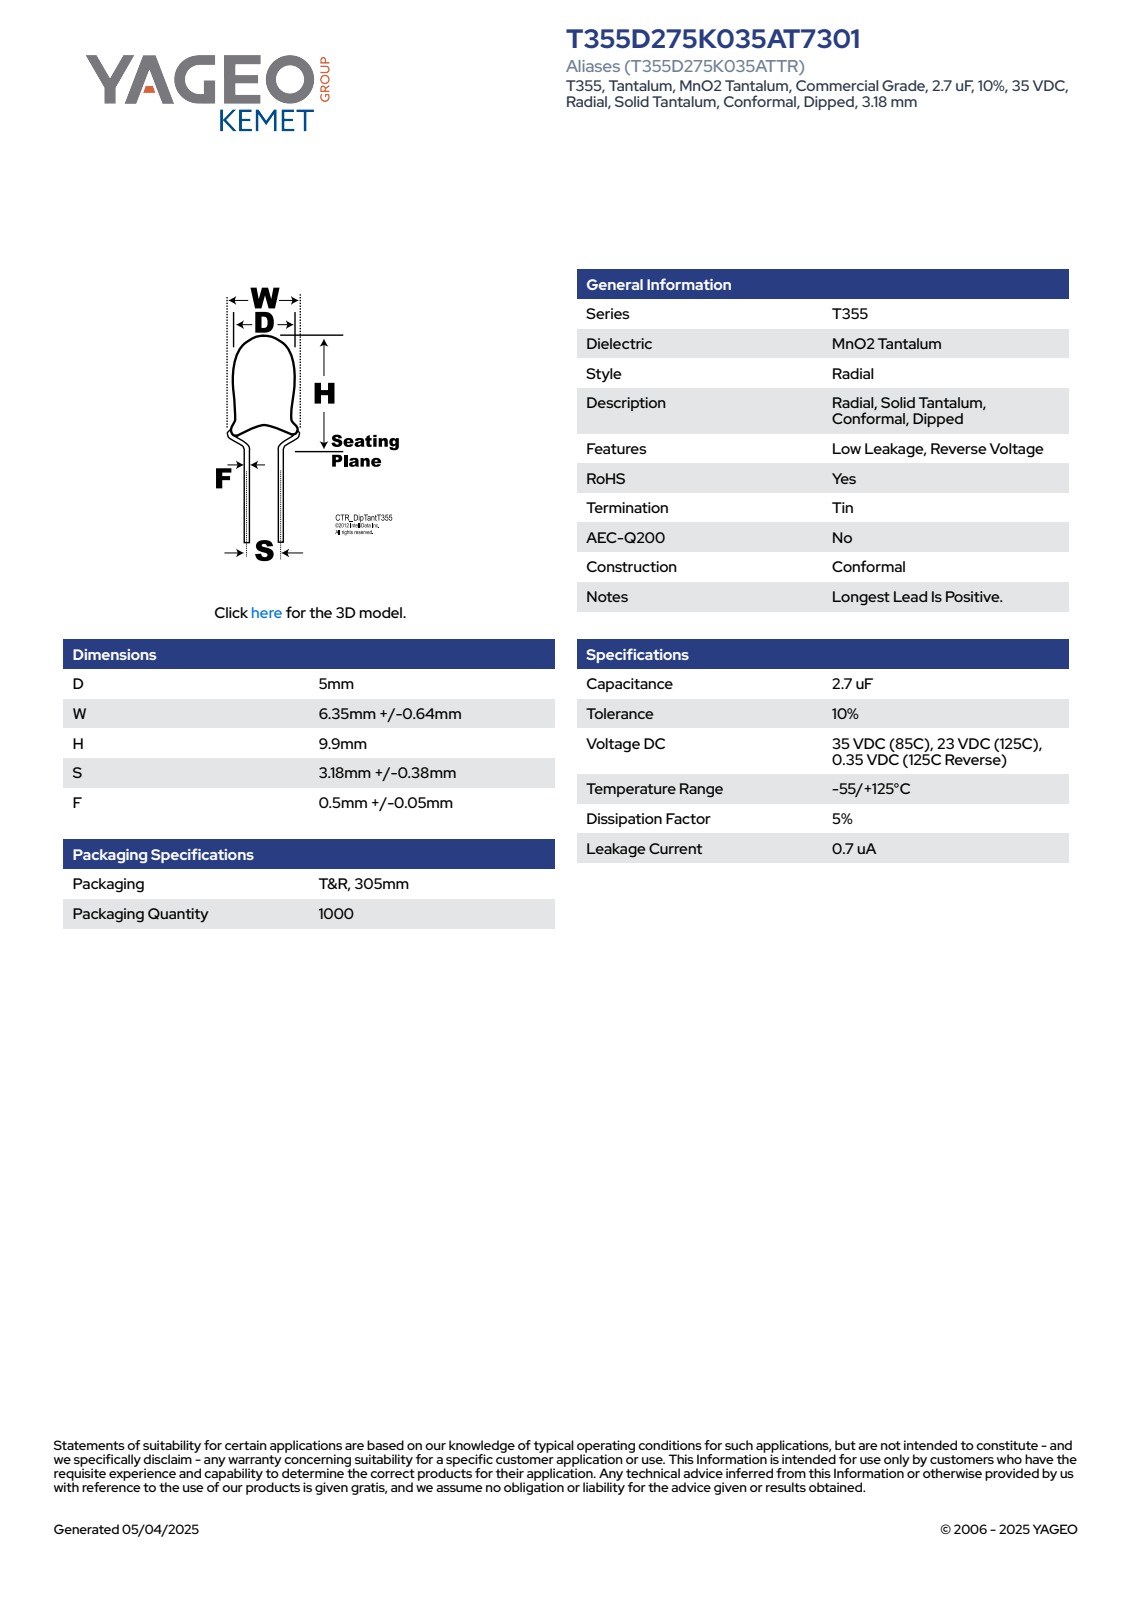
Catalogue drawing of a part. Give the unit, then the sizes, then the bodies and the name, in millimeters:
Units: millimetres
Overall size (bounding box): 15.46 × 6.99 × 5
Round bosses / shafts (diameter × count): ⌀5 ×1
Partial cylindrical surfaces — rounded edges, fillets, slot ends (radius × count): R2.49 ×1
Main face-to-face distances: 6.91, 8.55, 15.46, 12.39, 3.84, 3.07, 11.79, 3.24, 0.6, 3.67
Volume: 118 mm³ · Surface area: 159 mm²
Bodies: 1 solid, 100 faces (30 planar, 6 cylindrical, 64 other)
Part name (STEP PRODUCT): CTR_T355_D5W6.99H9.9S3.18LL5.56F0.55
STEP written by: SolidWorks 2021 (AUTOMOTIVE_DESIGN)
